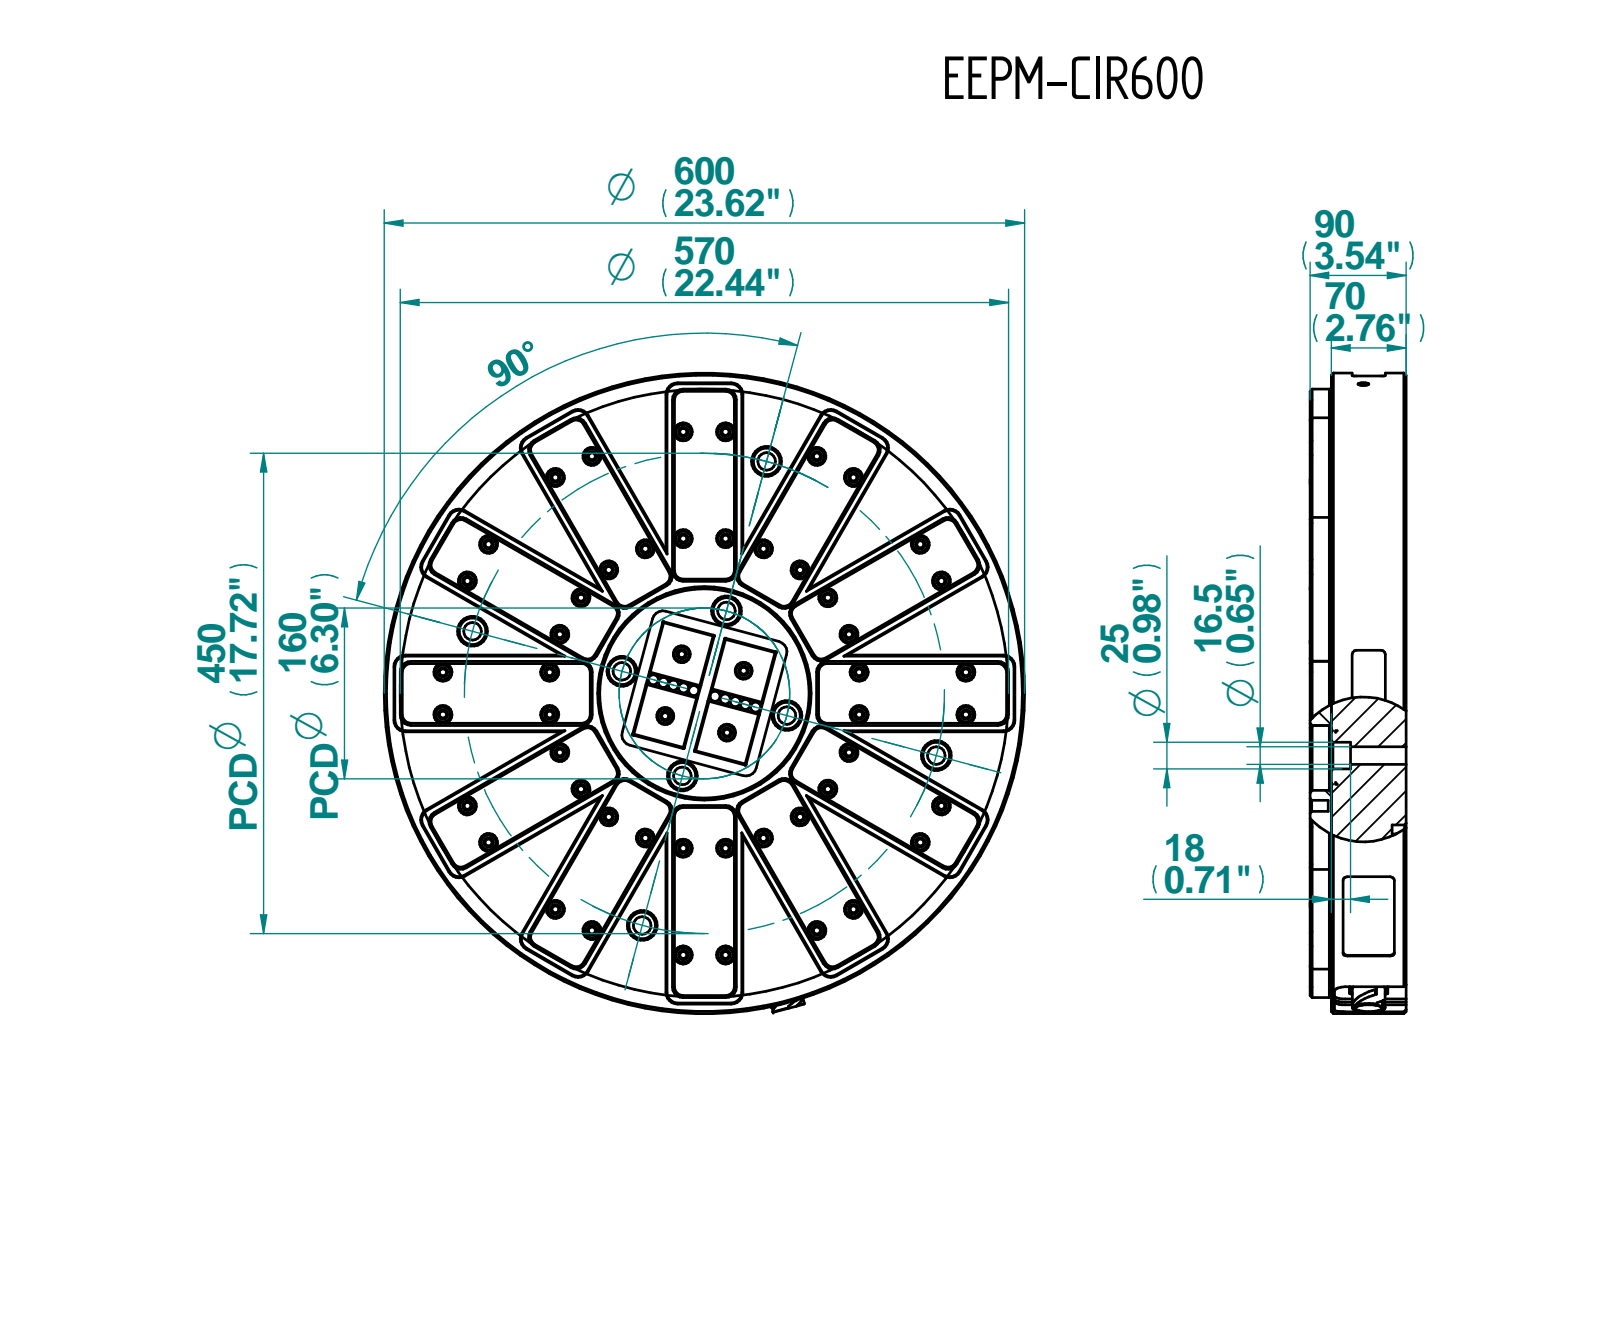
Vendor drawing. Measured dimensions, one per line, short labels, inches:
name: 開關頭+4PIN; 繪-4PIN\X2\958B95DC982\X0\; EEPM-IB220B-\X2\7D3052A05DE\X0\; EEPM-CIR600-規格品-\X2\7D3052A05DE\X0\ (+1 more)
written by: Unknown (AUTOMOTIVE_DESIGN)
unit: in
bodies: 16 solids, 1573 faces (739 planar, 506 cylindrical, 328 other)
size: 23.622 × 23.622 × 3.543
volume: 1 339 in³; area: 1 941 in²
holes: 52× ⌀0.262, 52× ⌀0.354, 52× ⌀0.551, 40× ⌀0.256, 40× ⌀0.433, 10× ⌀0.378, 9× ⌀0.984, 8× ⌀0.65, 5× ⌀0.097, 4× ⌀0.114, 4× ⌀0.126, 4× ⌀0.272
bosses: 4× ⌀0.138, 4× ⌀0.094, 1× ⌀23.622, 1× ⌀1.209, 1× ⌀1.181, 1× ⌀1.004
rounds: 80× R0.394, 24× R0.157, 2× R0.07, 2× R0.197, 2× R1.181
face distances: 2.756, 0.787, 3.543, 2.756, 0.788, 2.362, 0.197, 2.559, 0.118, 0.157
hole spacings: 0.774, 0.752, 1.063, 1.243, 1.412, 1.559, 4.235, 0.568
